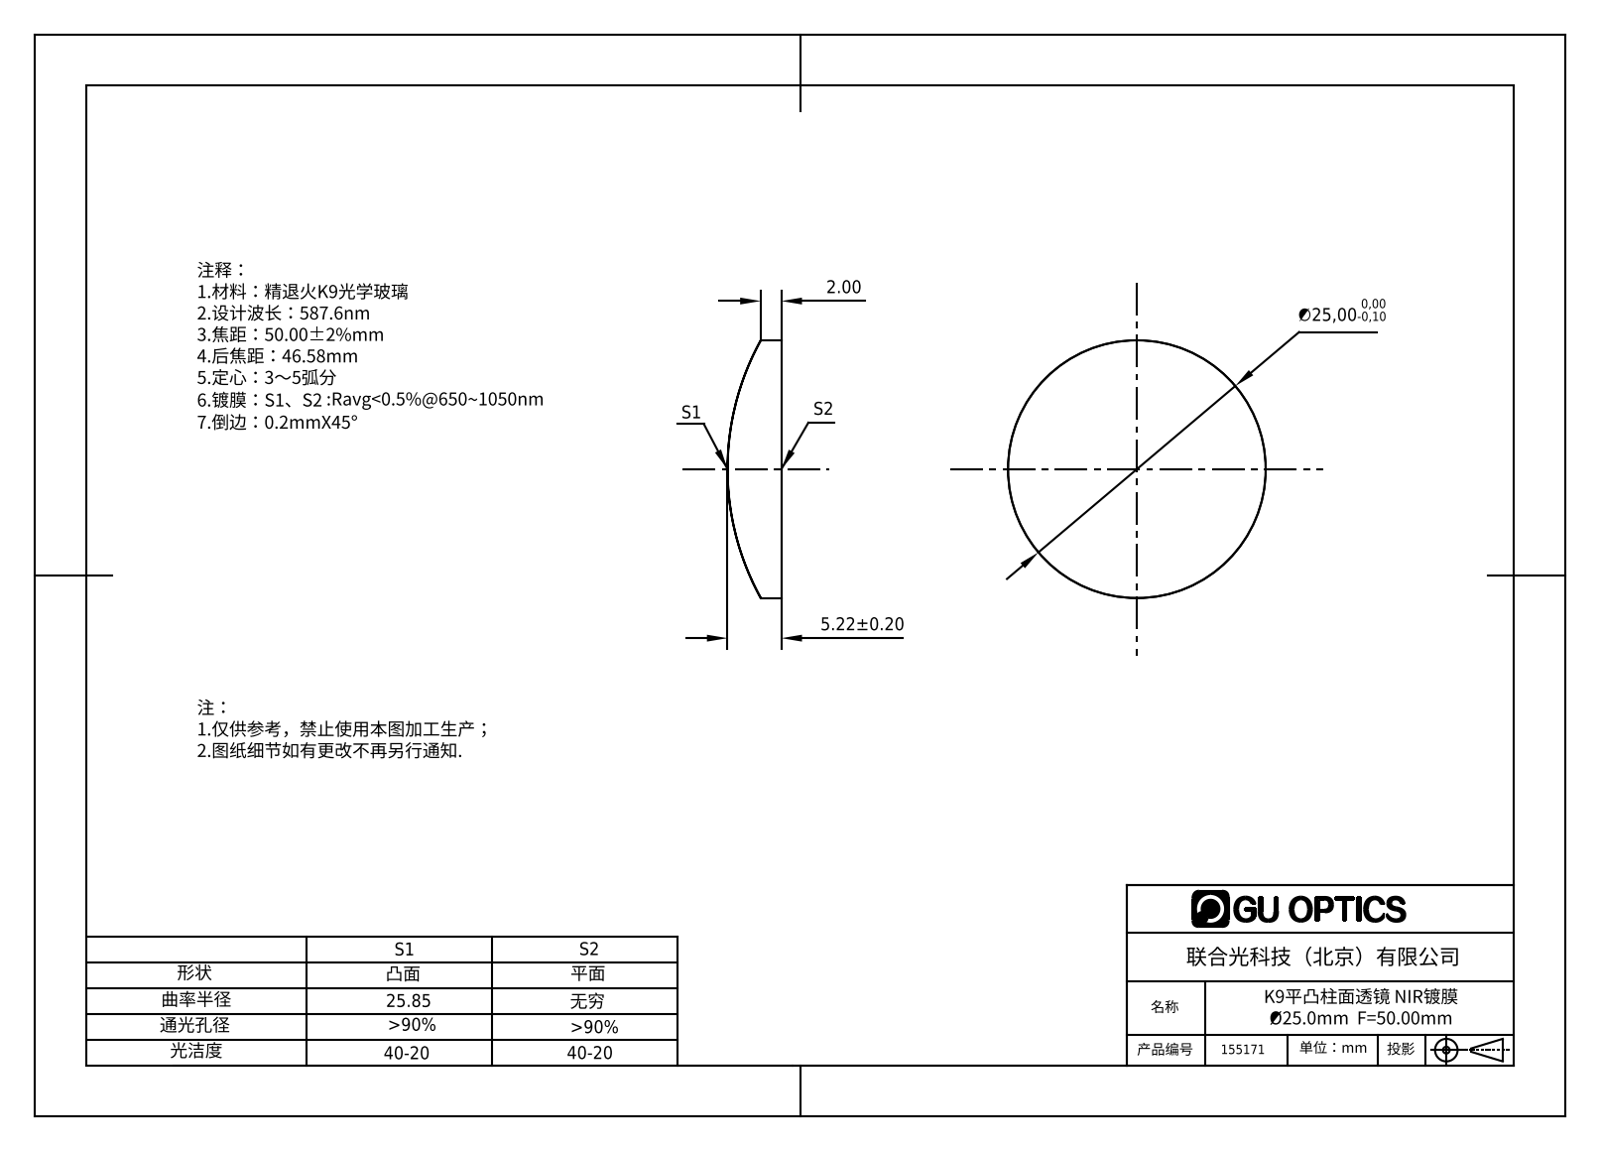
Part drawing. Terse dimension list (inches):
name: 155039
written by: SolidWorks 2016 (AUTOMOTIVE_DESIGN)
unit: in
bodies: 1 solid, 4 faces (1 planar, 3 cylindrical, 0 other)
size: 0.984 × 0.984 × 0.206
volume: 0.133 in³; area: 1.989 in²
bosses: 1× ⌀0.984
rounds: 1× R1.018
